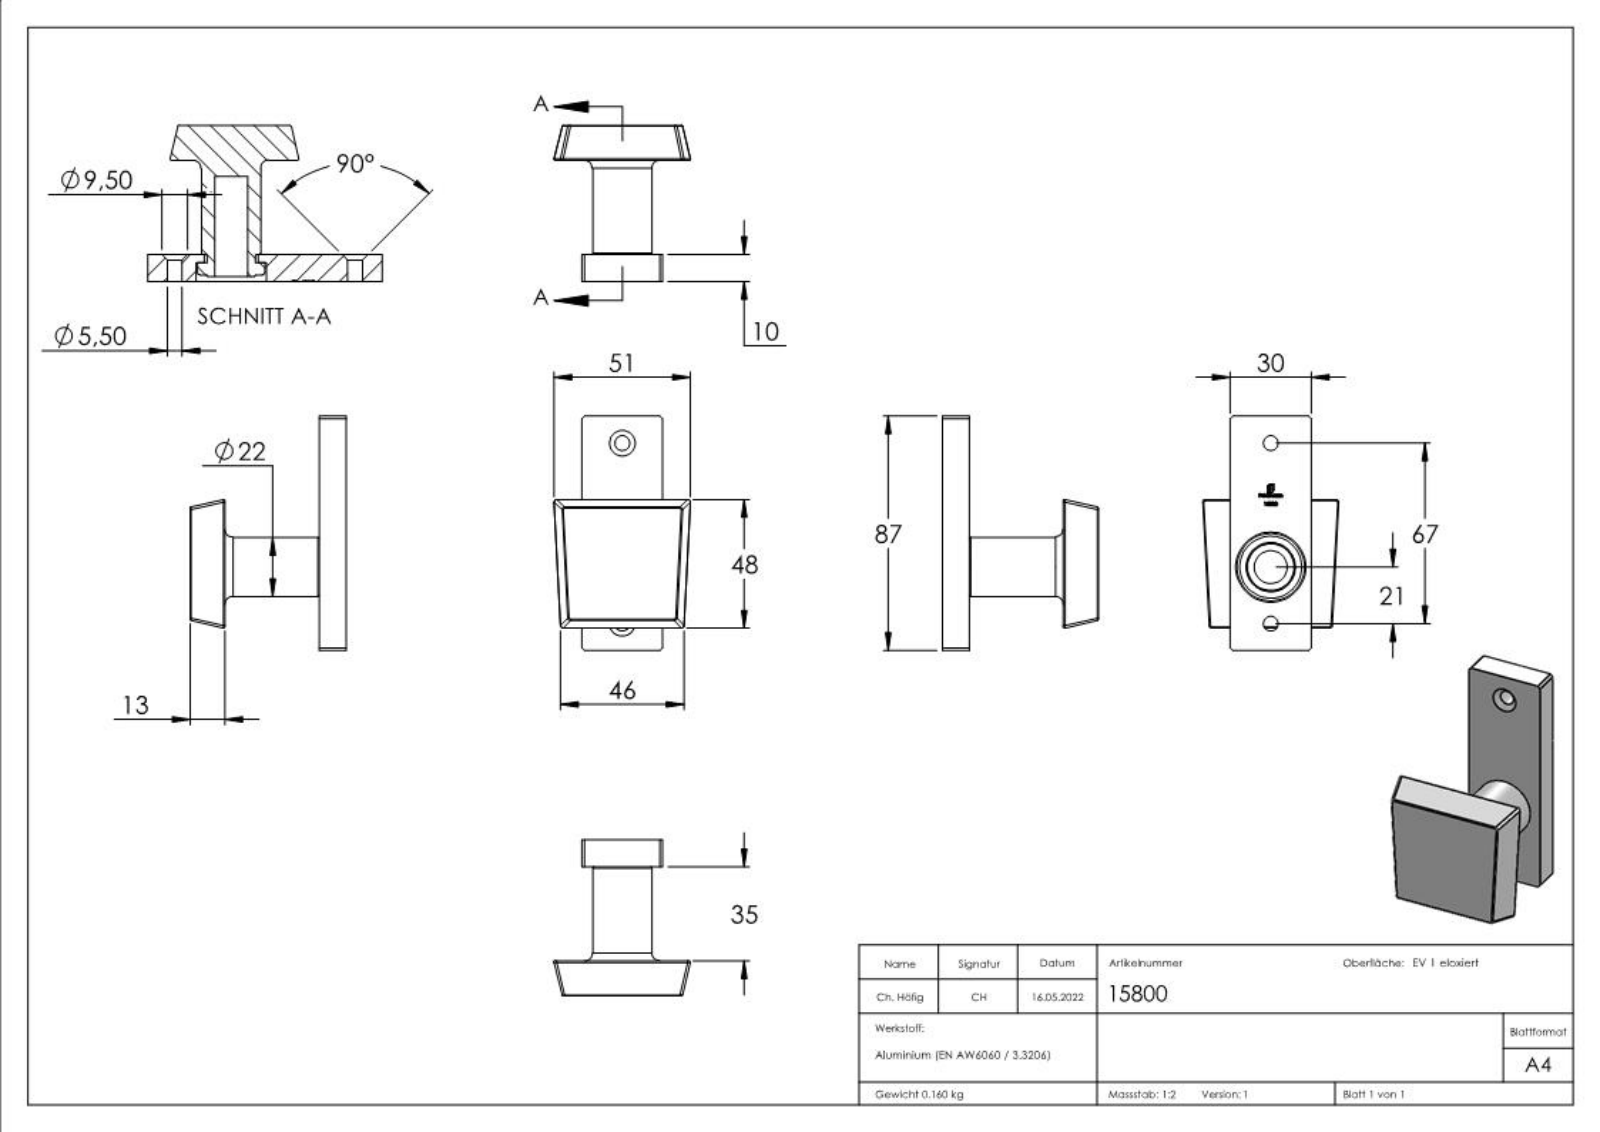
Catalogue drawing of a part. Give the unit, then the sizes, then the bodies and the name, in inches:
Units: inches
Overall size (bounding box): 3.425 × 2.283 × 1.889
Round holes (diameter × count): ⌀0.217 ×2, ⌀0.48 ×1, ⌀0.787 ×1, ⌀1.024 ×1
Round bosses / shafts (diameter × count): ⌀0.984 ×1, ⌀0.906 ×1, ⌀0.701 ×1
Partial cylindrical surfaces — rounded edges, fillets, slot ends (radius × count): R0.02 ×8, R0.039 ×4
Main face-to-face distances: 0.394, 2.283, 1.89, 1.693, 1.299, 0.591, 1.181, 0.276, 0.118, 1.417
Hole centre spacings: 0.827, 1.811, 2.638
Volume: 3.772 in³ · Surface area: 29.38 in²
Bodies: 2 solids, 278 faces (131 planar, 20 cylindrical, 127 other)
Part name (STEP PRODUCT): 15800 Teil1_15800 Teil1; 15800 Teil2_15842 Teil2; 15800
STEP written by: SolidWorks 2018 (CONFIG_CONTROL_DESIGN)
